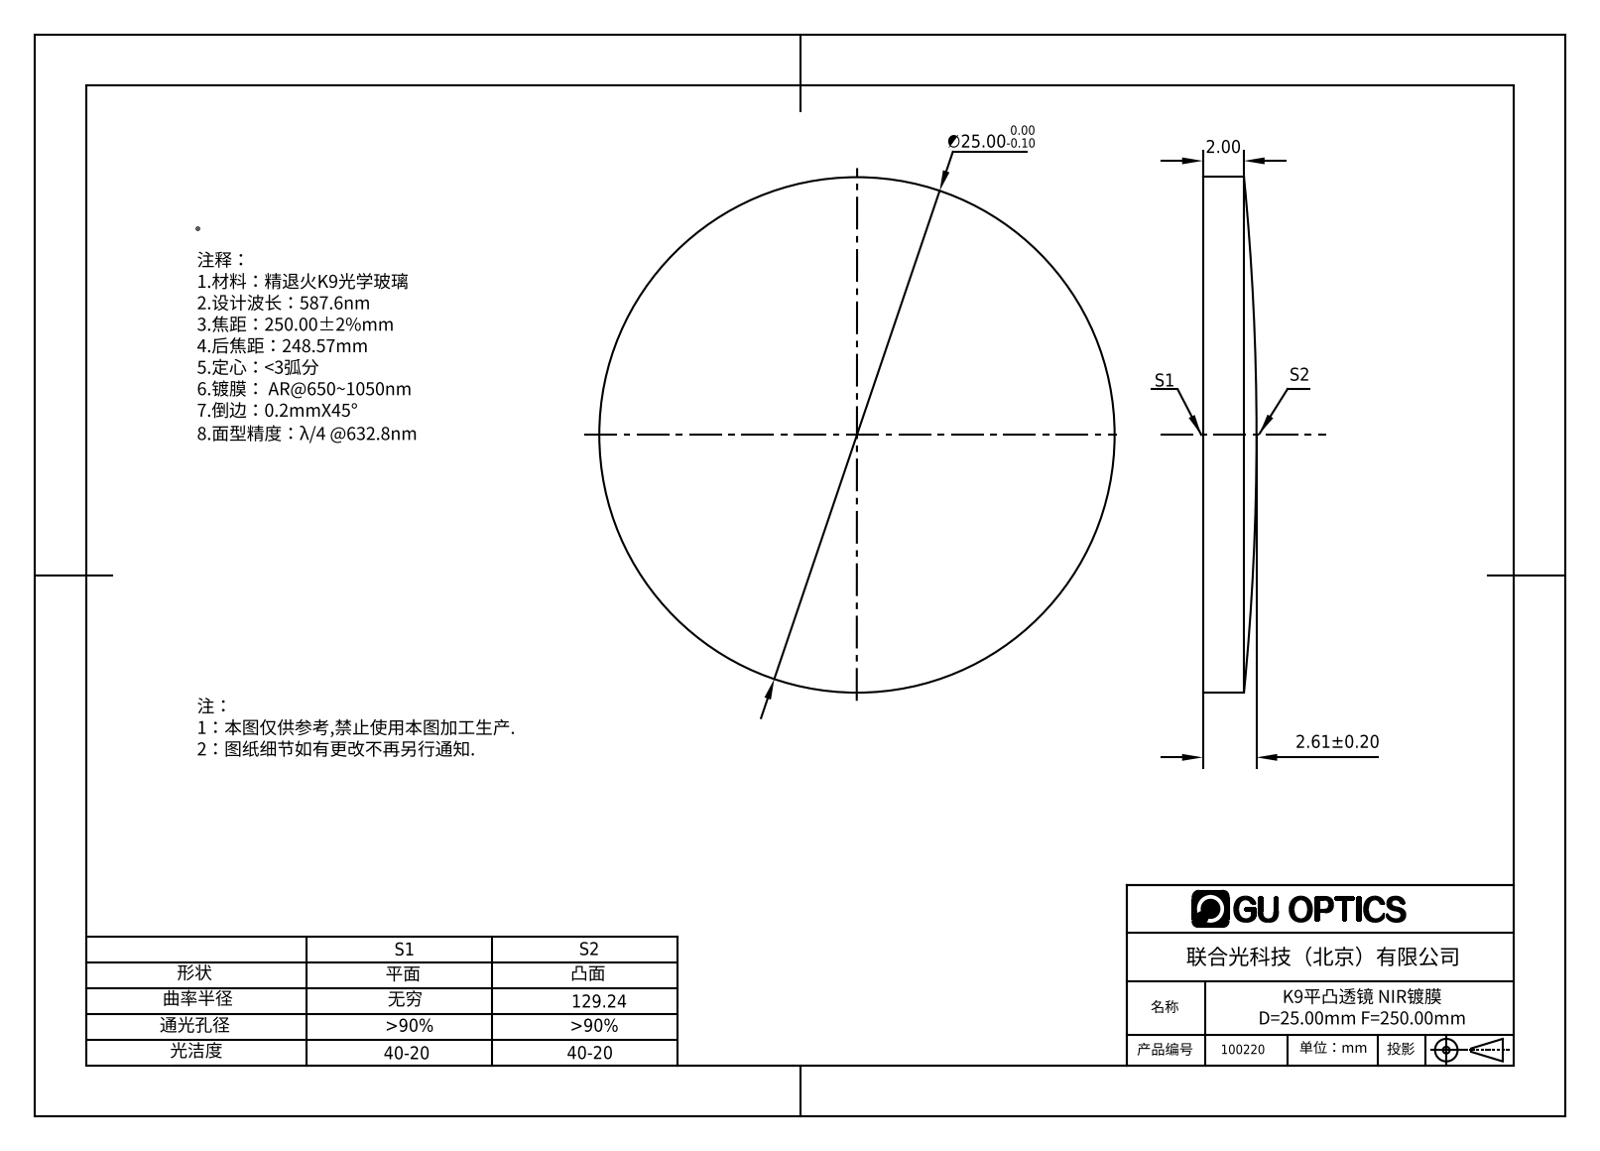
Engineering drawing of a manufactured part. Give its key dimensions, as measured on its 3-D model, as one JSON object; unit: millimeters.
{"part_name": "100220", "step_written_by": "SolidWorks 2016 (AUTOMOTIVE_DESIGN)", "units": "millimeters", "bodies": {"solids": 1, "faces": 5, "planar": 1, "cylindrical": 2, "other": 2}, "overall_size": [25, 25, 2.61], "volume_mm3": 1132, "surface_area_mm2": 1140, "round_bosses_or_shafts": [[25, 1]]}
